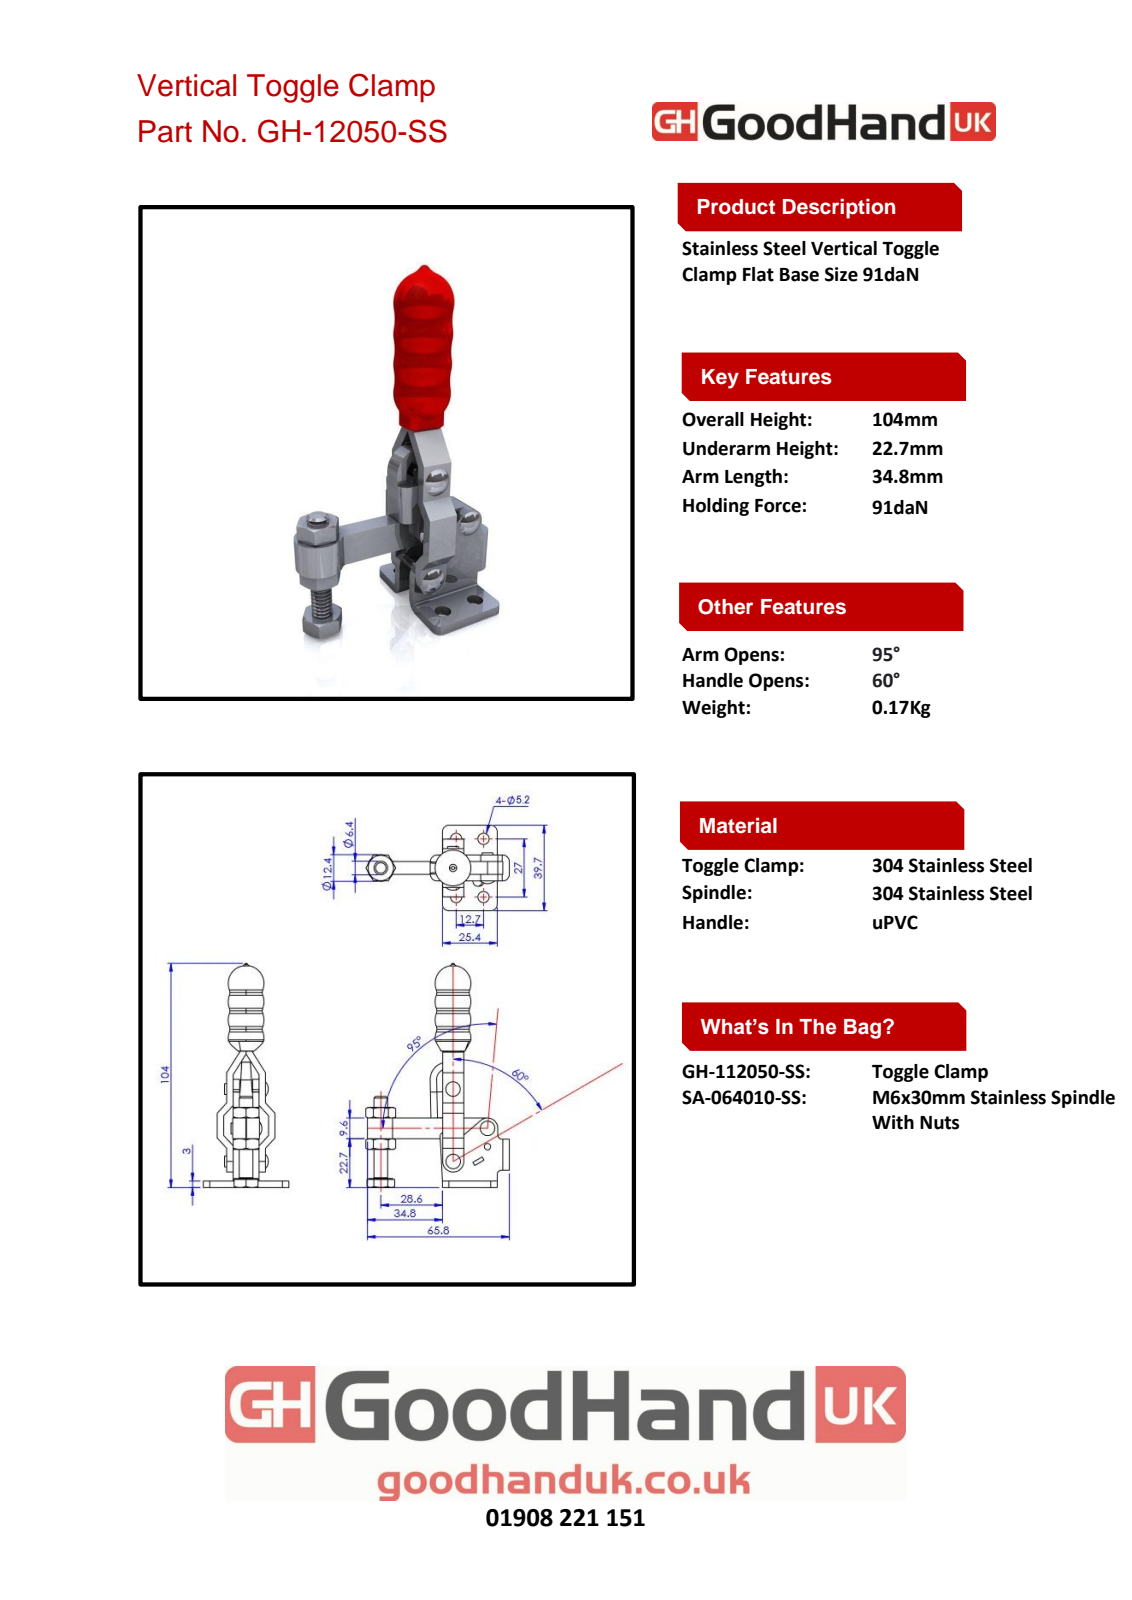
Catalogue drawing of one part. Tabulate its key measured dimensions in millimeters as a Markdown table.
| quantity | value |
| --- | --- |
| part name | Group1^GH-12050-SS(簡化)-1; GH-12050-SS(簡化)-1; 11205008-1^GH-12050-SS(簡化)-1; Group3^GH-12050-SS(簡化)-1 (+2 more) |
| STEP written by | SolidWorks 2016 (AUTOMOTIVE_DESIGN) |
| units | millimeters |
| bodies | 5 solids, 298 faces (123 planar, 96 cylindrical, 79 other) |
| overall size | 104 × 66.1 × 39.7 |
| volume | 25 562 mm³ |
| surface area | 16 906 mm² |
| round holes (diameter × count) | 3 × 4, 5.2 × 4, 6.4 × 1 |
| round bosses / shafts (diameter × count) | 5 × 4, 12.4 × 1, 10 × 1, 6 × 1 |
| partial cylindrical surfaces (radius × count) | 2 × 4, 3 × 4, 1 × 2, 4.5 × 2, 5 × 2, 1.5 × 1, 2.5 × 1, 4.8 × 1 |
| main face-to-face distances | 3, 9, 6, 12, 19.4, 29.25, 4.4, 7.4, 16.4, 22.65 |
| hole center spacings | 12.7, 27, 29.84, 37.47, 49.53, 15.2, 15.59, 18.4 |
